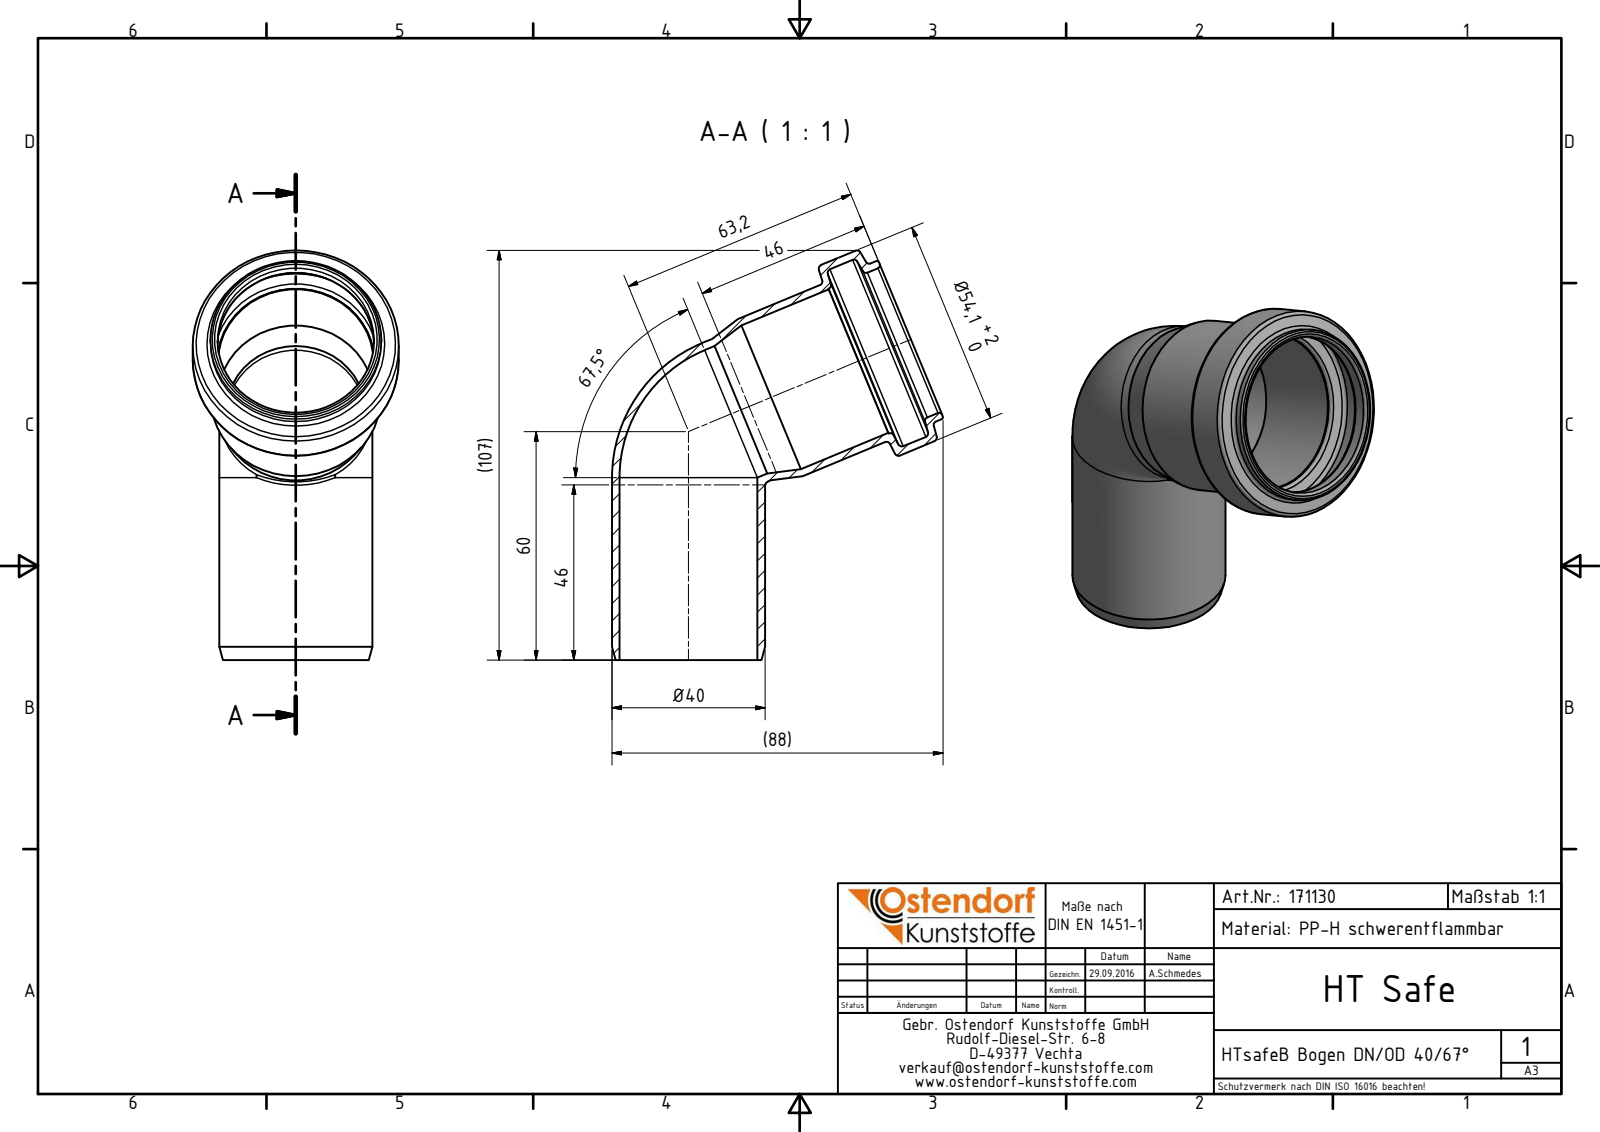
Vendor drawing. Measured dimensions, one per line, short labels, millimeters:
name: 171130 HTsafeB DN_OD 40_67°
written by: Autodesk Inventor 2016 (AUTOMOTIVE_DESIGN)
unit: mm
bodies: 1 solid, 34 faces (3 planar, 11 cylindrical, 20 other)
size: 107.54 × 86.93 × 54.1
volume: 31 185 mm³; area: 33 265 mm²
holes: 2× ⌀36.2, 2× ⌀41.1, 1× ⌀40.8, 1× ⌀50.3
bosses: 2× ⌀40.2, 1× ⌀54.1, 1× ⌀44.9, 1× ⌀44.6
face distances: 14.91
